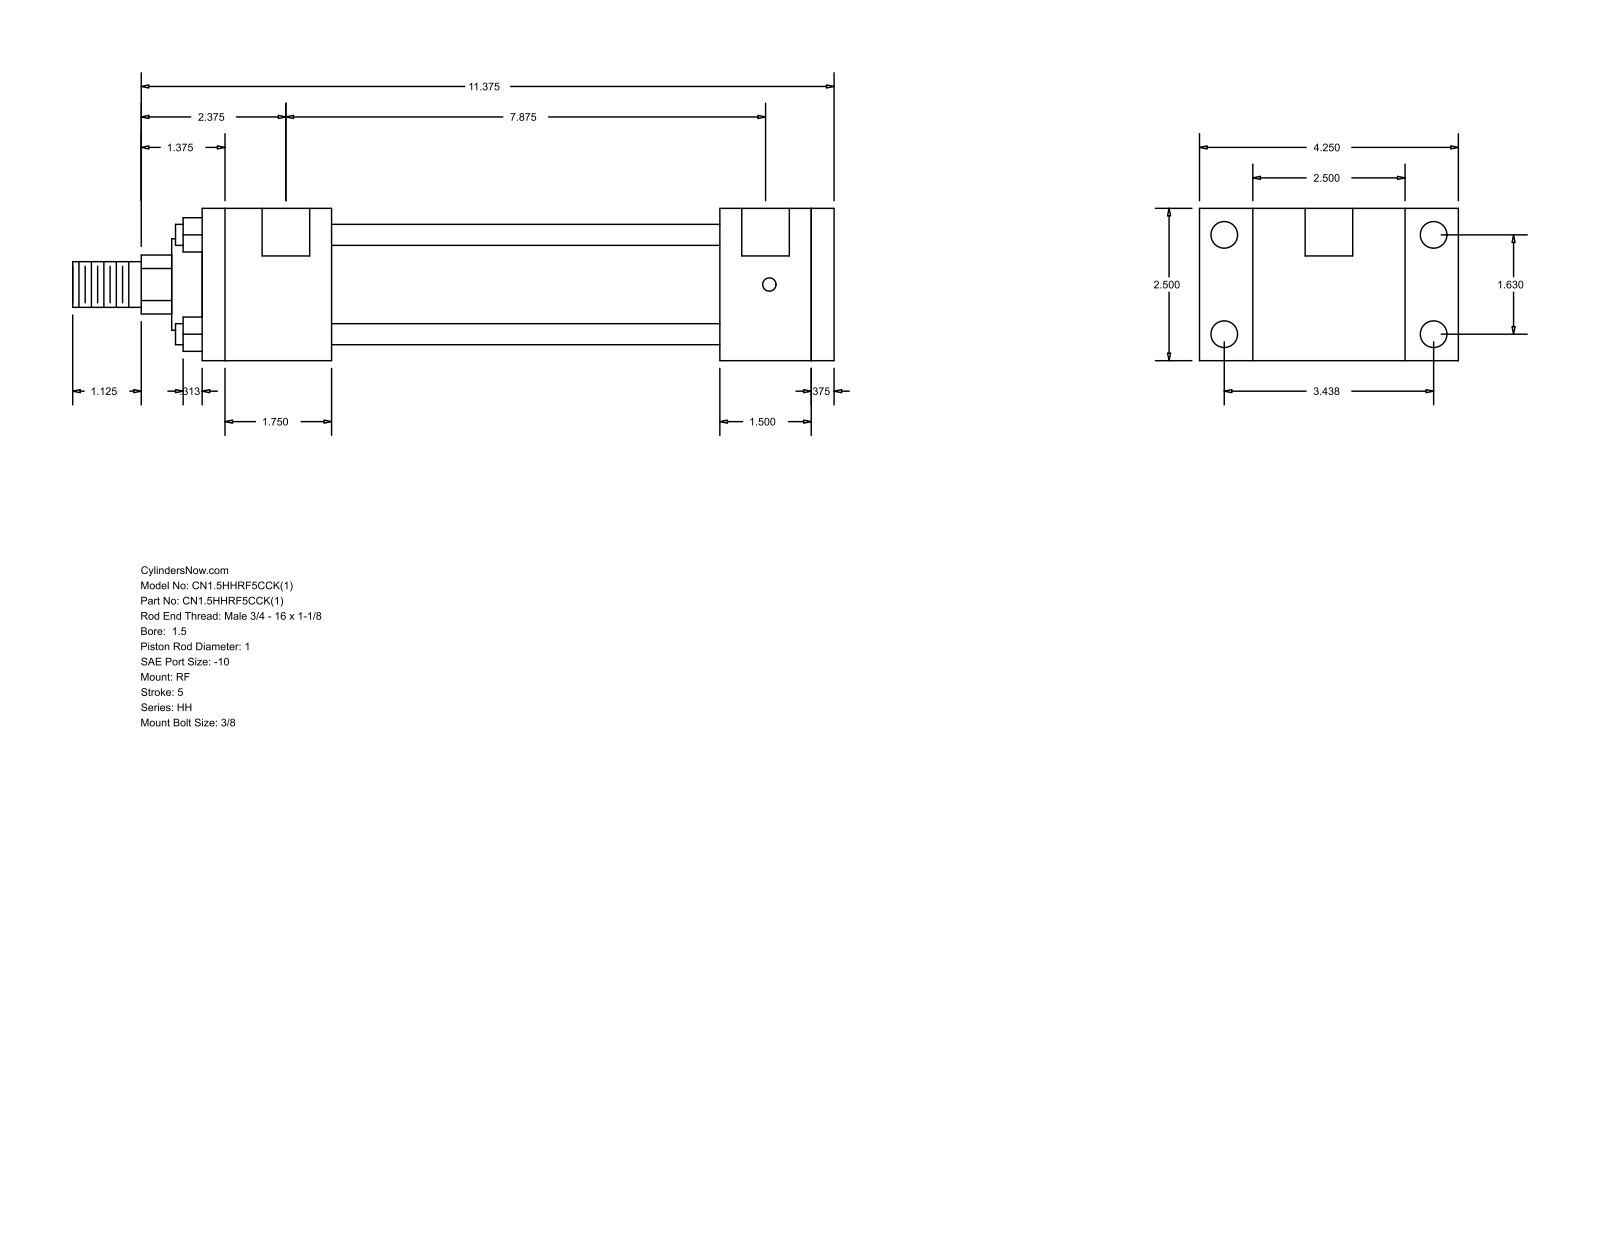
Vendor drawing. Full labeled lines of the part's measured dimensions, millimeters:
Part name (STEP PRODUCT): HH_RF__0150_1
STEP written by: GSSL Pune (CONFIG_CONTROL_DESIGN)
Units: millimetres
Bodies: 0 solids, 92 faces (64 planar, 28 cylindrical, 0 other)
Overall size (bounding box): 317.5 × 107.95 × 63.5
Round holes (diameter × count): ⌀5.56 ×4, ⌀11.13 ×4, ⌀19.84 ×2
Round bosses / shafts (diameter × count): ⌀8.76 ×4, ⌀44.45 ×1, ⌀38.1 ×1, ⌀25.4 ×1, ⌀19.05 ×1
Partial cylindrical surfaces — rounded edges, fillets, slot ends (radius × count): R12.29 ×1
Main face-to-face distances: 63.5, 9.53, 38.1, 161.92, 200.02, 209.55, 47.63, 53.98, 215.9, 254
Hole centre spacings: 1.59, 41.4, 87.32, 96.64, 201.61, 203.2, 200.02
